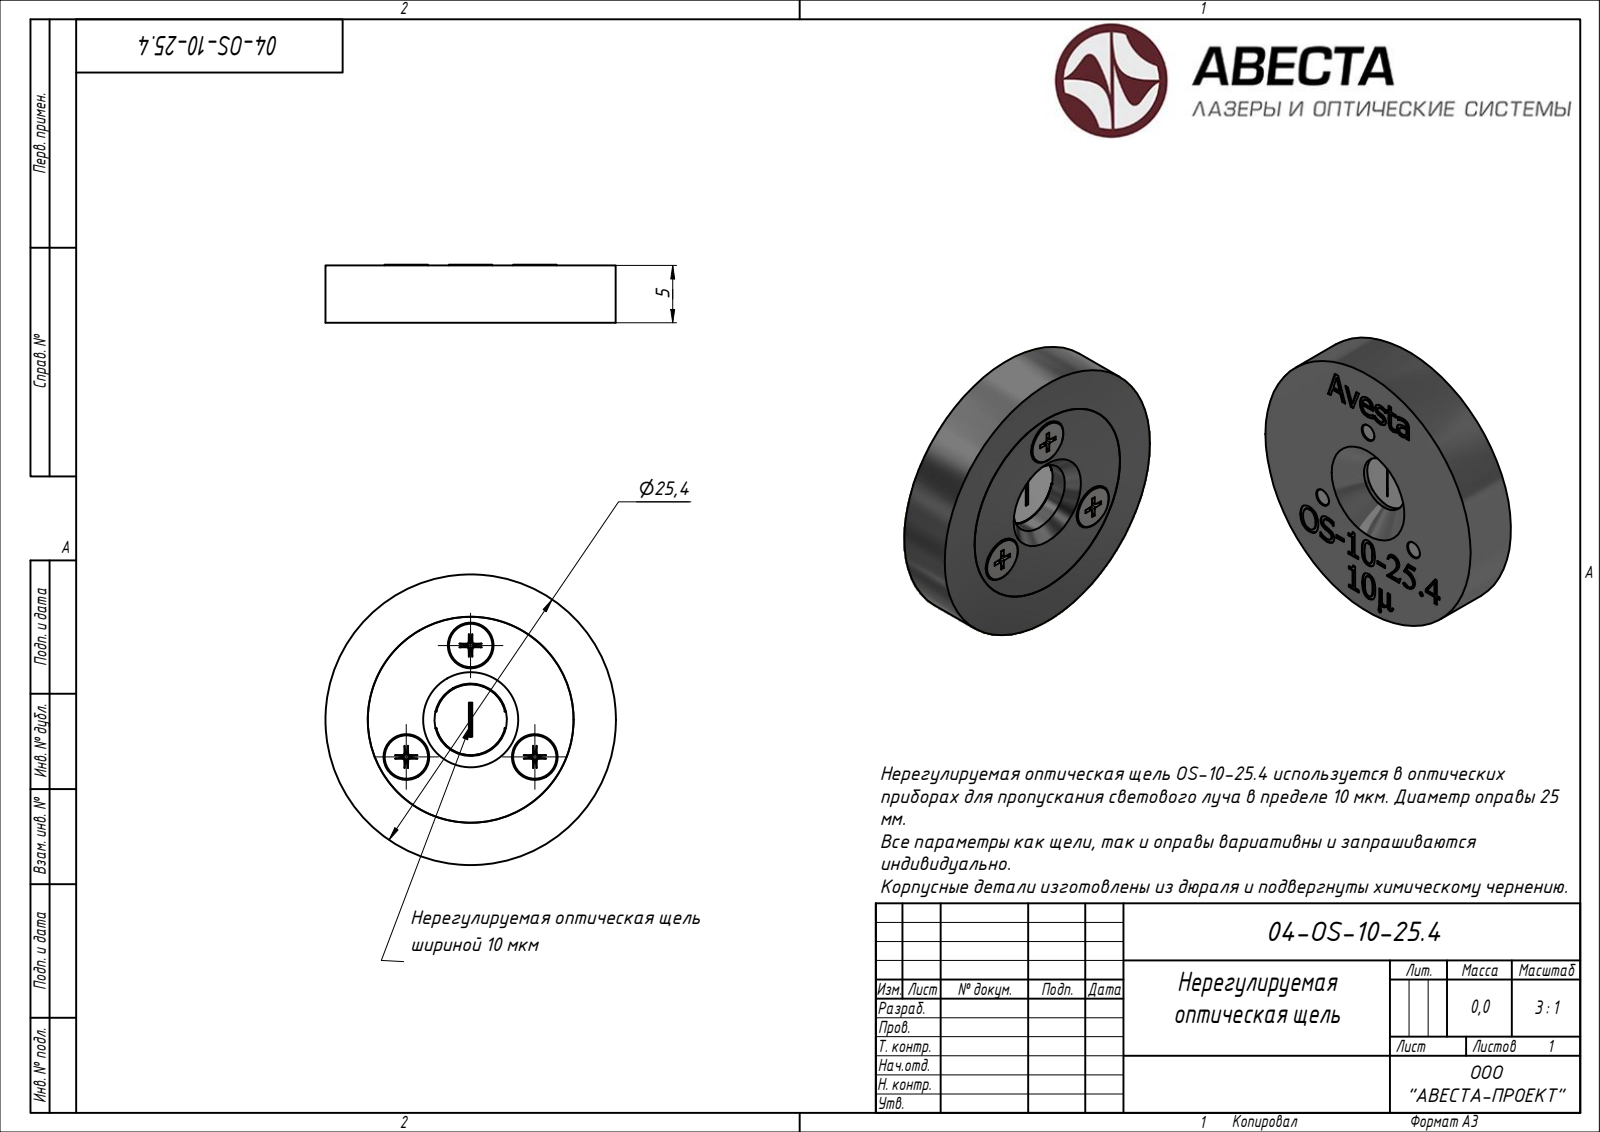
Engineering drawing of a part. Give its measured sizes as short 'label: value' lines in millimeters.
written by: ST-DEVELOPER v15 (AUTOMOTIVE_DESIGN)
unit: mm
bodies: 1 solid, 420 faces (0 planar, 0 cylindrical, 420 other)
size: 25.4 × 25.4 × 5.08
volume: 2 360 mm³; area: 1 519 mm²
